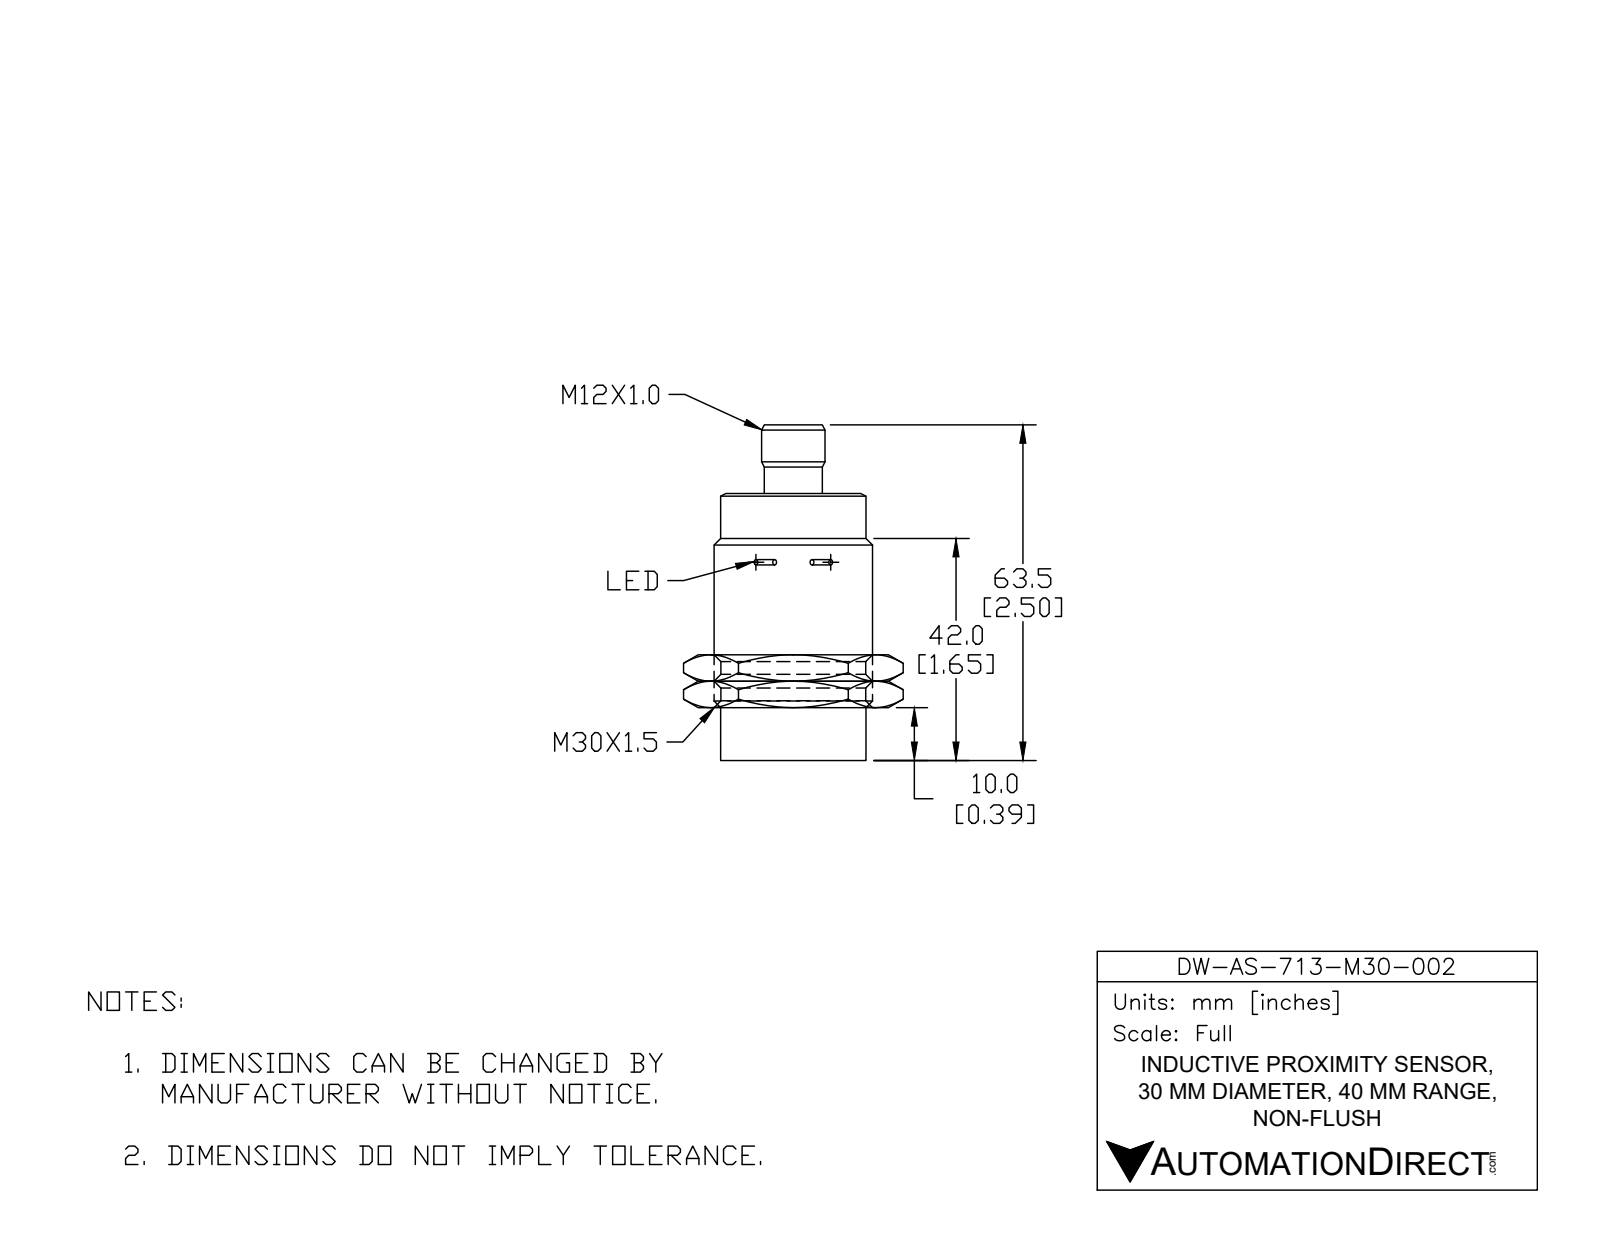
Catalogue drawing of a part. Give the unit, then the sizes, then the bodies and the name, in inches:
Units: inches
Overall size (bounding box): 2.502 × 1.181 × 1.181
Round holes (diameter × count): ⌀0.12 ×2, ⌀0.335 ×1
Round bosses / shafts (diameter × count): ⌀0.043 ×4, ⌀1.181 ×1, ⌀1.083 ×1, ⌀0.472 ×1, ⌀0.415 ×1
Partial cylindrical surfaces — rounded edges, fillets, slot ends (radius × count): R0.019 ×2, R0.022 ×1, R0.178 ×1, R0.193 ×1
Main face-to-face distances: 1.988, 2.159, 0.171, 1.654, 0.335, 0.506, 0.394, 1.26, 1.594, 1.766
Volume: 2.093 in³ · Surface area: 10.73 in²
Bodies: 1 solid, 51 faces (14 planar, 27 cylindrical, 10 other)
Part name (STEP PRODUCT): DW-AS-713-M30-002
STEP written by: SolidWorks 2017 (AUTOMOTIVE_DESIGN)
